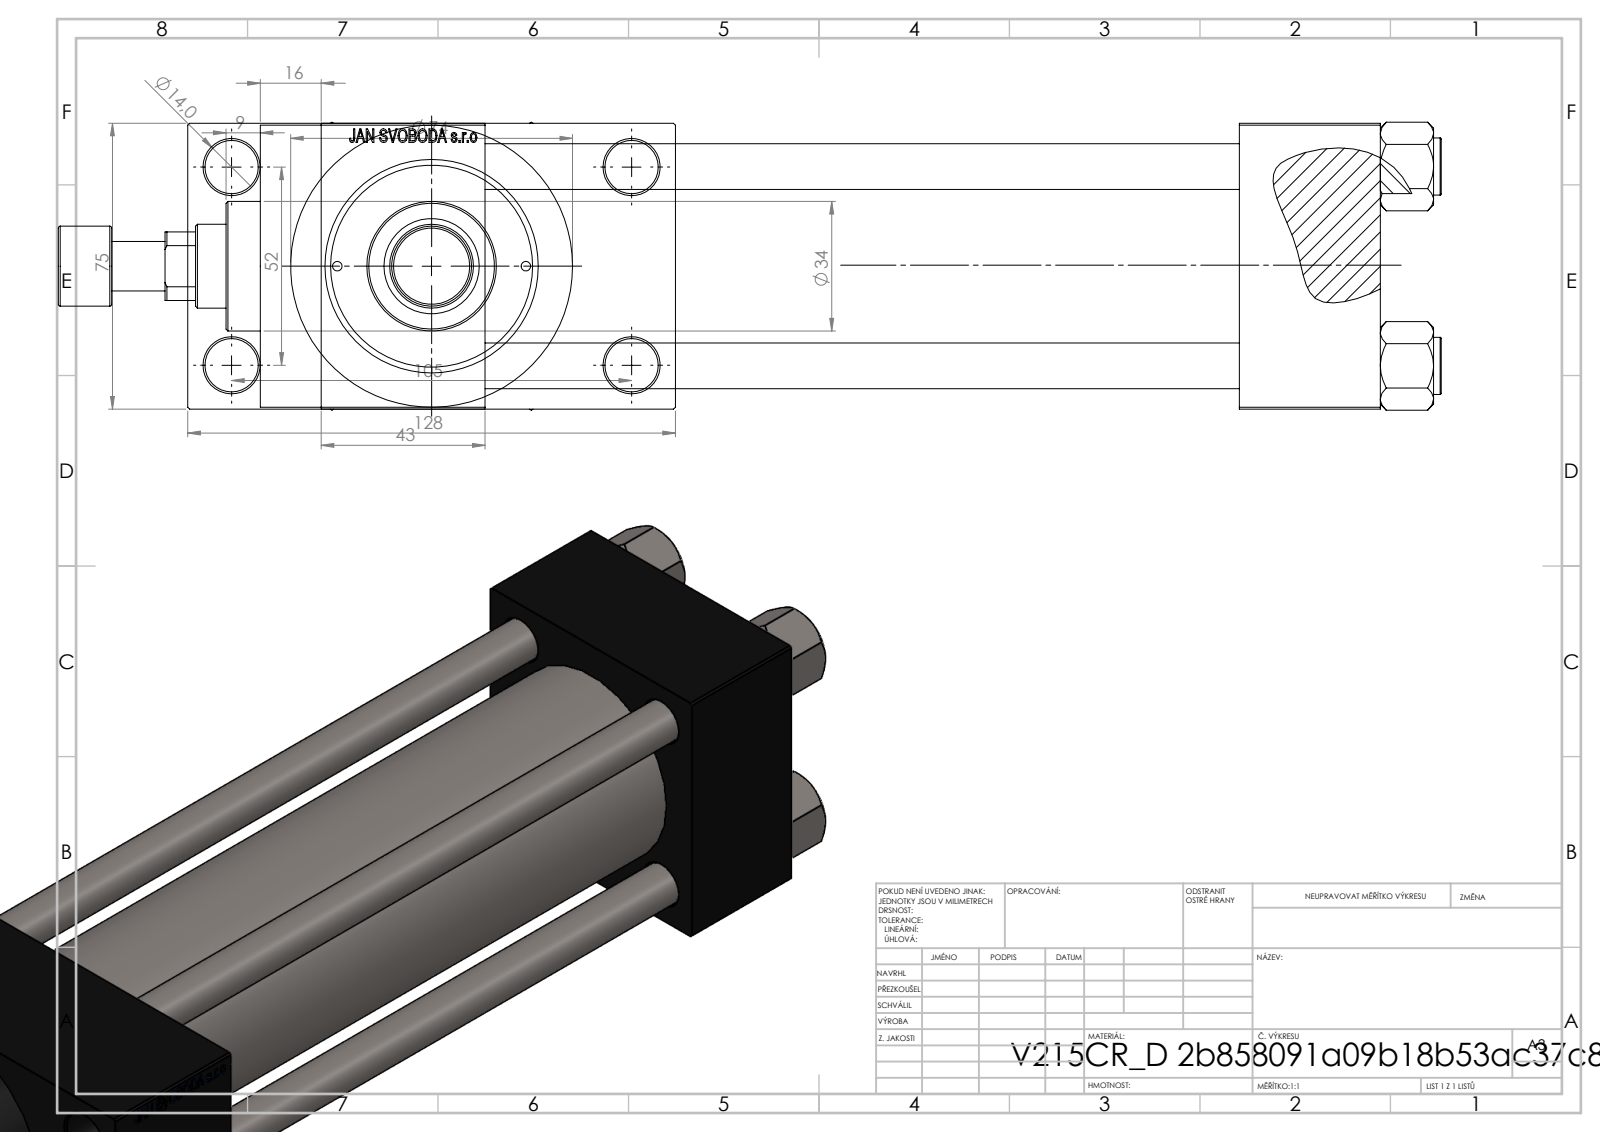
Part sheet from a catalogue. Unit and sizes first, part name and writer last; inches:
Units: inches
Overall size (bounding box): 14.291 × 5.039 × 2.974
Round holes (diameter × count): ⌀0.472 ×4, ⌀0.551 ×4, ⌀0.098 ×2, ⌀0.276 ×2, ⌀0.825 ×2, ⌀1.181 ×2, ⌀0.413 ×1, ⌀0.866 ×1, ⌀0.984 ×1, ⌀1.614 ×1, ⌀1.969 ×1, ⌀2.087 ×1
Round bosses / shafts (diameter × count): ⌀0.591 ×4, ⌀2.913 ×1, ⌀2.205 ×1, ⌀1.339 ×1, ⌀0.827 ×1, ⌀0.512 ×1
Main face-to-face distances: 2.953, 7.795, 1.457, 9.252, 1.043, 10.945, 9.488, 1.693, 3.996, 0.63
Hole centre spacings: 1.031, 1.037, 1.456, 1.497, 2.059, 2.253, 2.3, 2.307
Volume: 60.44 in³ · Surface area: 381.6 in²
Bodies: 12 solids, 1122 faces (502 planar, 96 cylindrical, 524 other)
Part name (STEP PRODUCT): V215CR_D_Body; V215CR_D_TYCINKA; V215_VC_A; NUT_M5_D (+2 more)
STEP written by: SolidWorks 2019 (CONFIG_CONTROL_DESIGN)
